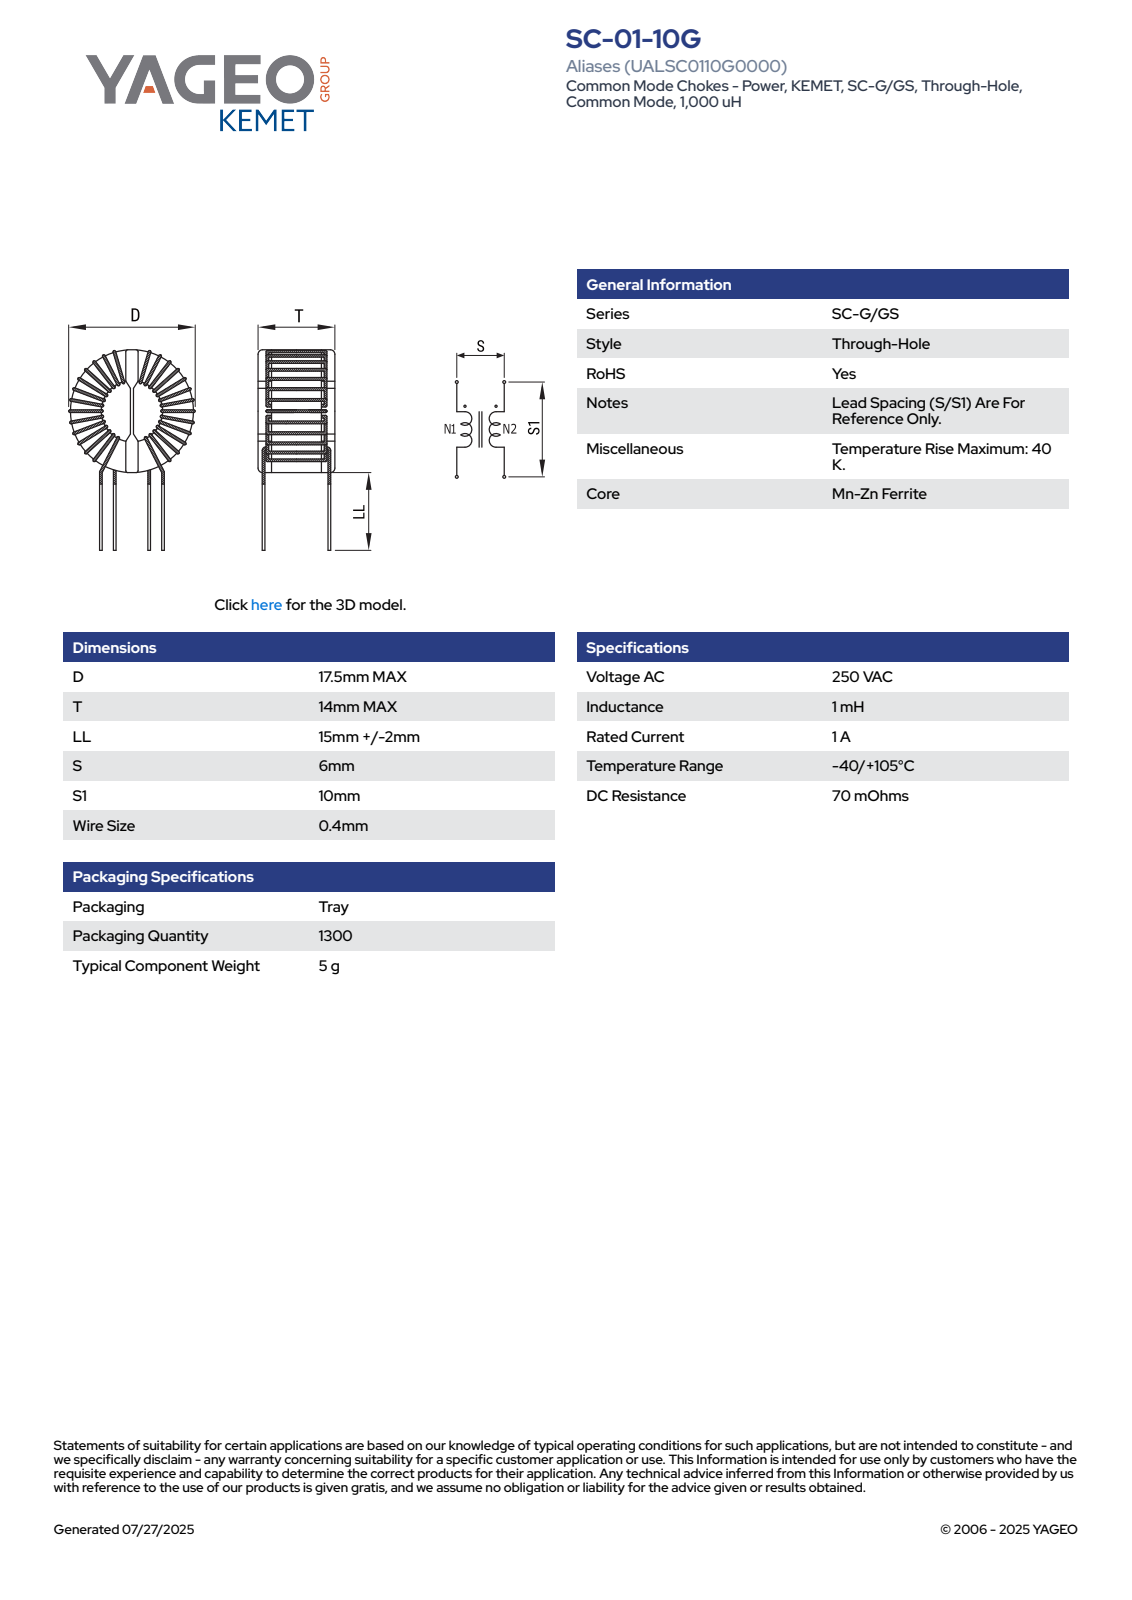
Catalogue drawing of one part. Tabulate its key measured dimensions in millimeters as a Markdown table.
| quantity | value |
| --- | --- |
| part name | SC-01-10G |
| STEP written by | SolidWorks 2018 (AUTOMOTIVE_DESIGN) |
| units | millimeters |
| bodies | 1 solid, 268 faces (121 planar, 65 cylindrical, 82 other) |
| overall size | 30.37 × 17.5 × 14 |
| volume | 1 786 mm³ |
| surface area | 1 710 mm² |
| round bosses / shafts (diameter × count) | 0.4 × 8 |
| partial cylindrical surfaces (radius × count) | 0.2 × 16, 2.32 × 1, 3.21 × 1, 3.62 × 1, 3.67 × 1, 3.8 × 1, 6.35 × 1, 6.4 × 1 |
| main face-to-face distances | 1.2, 2, 8.3, 0.8, 3.2, 2.85, 11.15, 1.15, 2.05, 0.85 |
